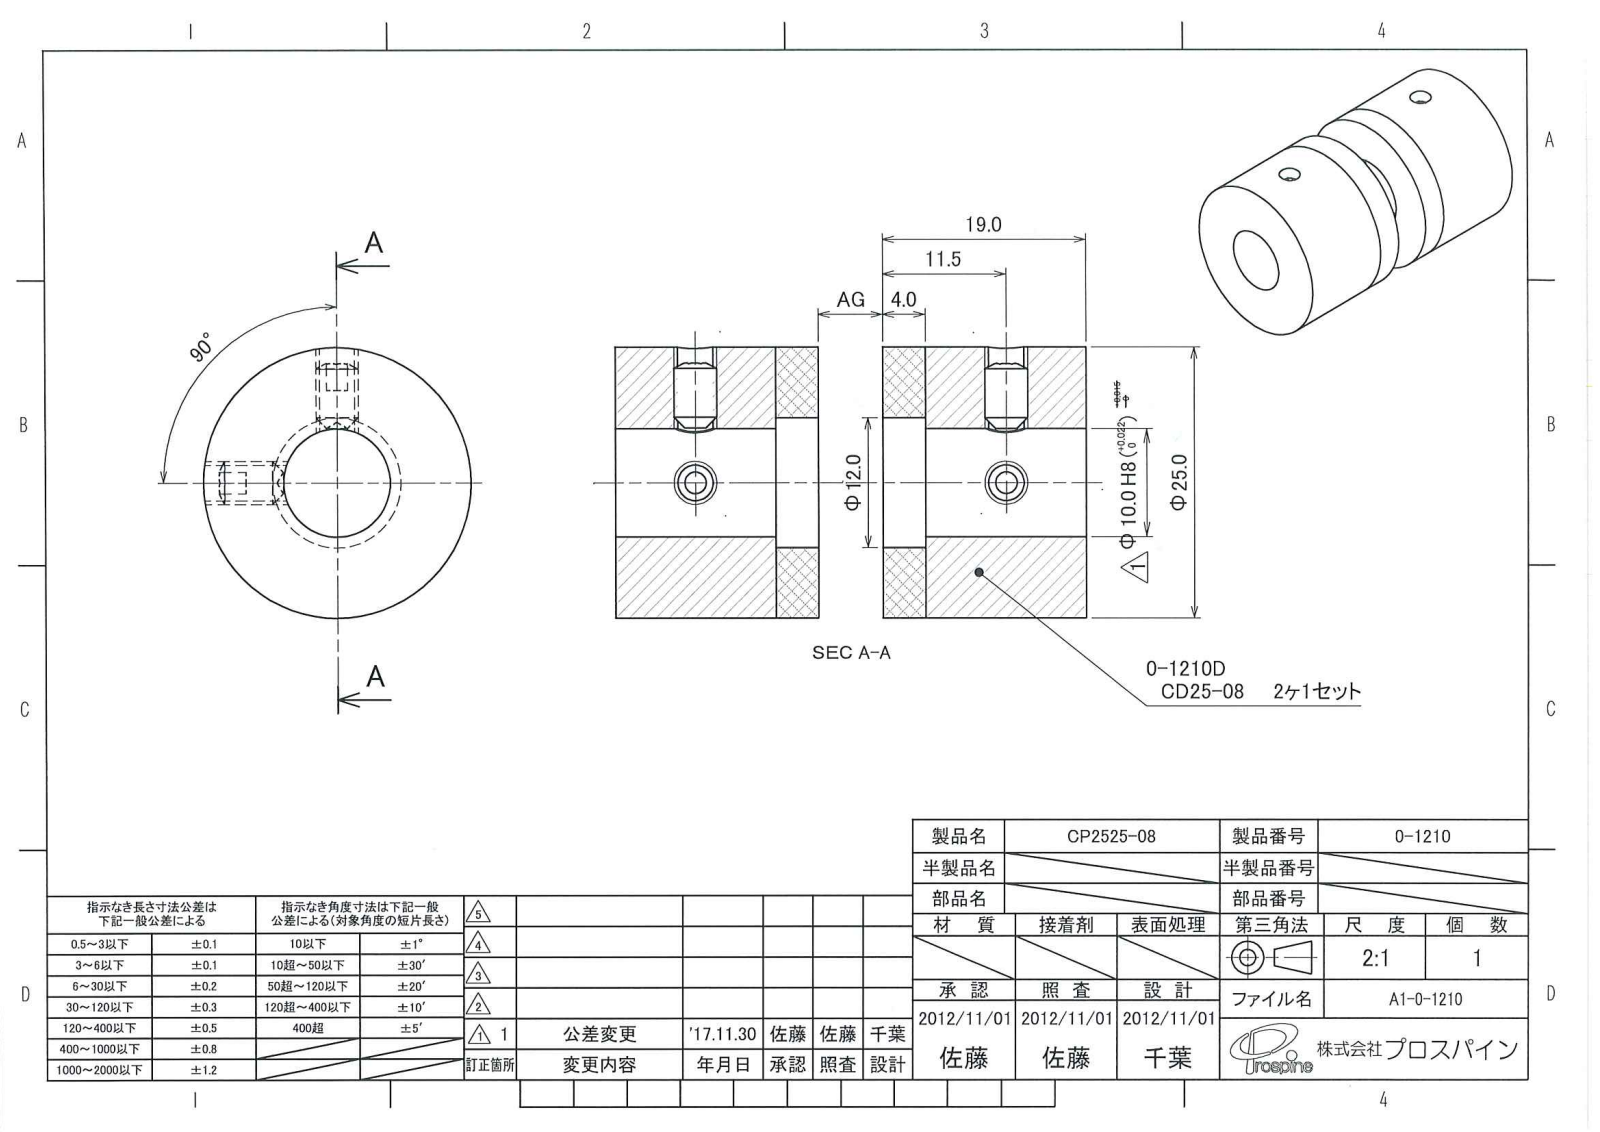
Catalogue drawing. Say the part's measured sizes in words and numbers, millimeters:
Its 3-D file was written by "PSStep 10.0 (CONFIG_CONTROL_DESIGN)". It is 5 solids with 43 faces: 25 planar, 9 cylindrical and 9 other. Overall it measures 25 by 25 by 21 millimeters. Its volume is 7 742 cubic millimeters and its surface area 4 130 square millimeters. Round holes: 2 of diameter 3.3, 1 of diameter 10, 1 of diameter 12. Round bosses or shafts: 3 of diameter 4, 1 of diameter 25. The main face-to-face distances are 15, 19, 4, 2, 1.99, 7.5, 9.5, 18.5, 3.5, 0.5.
